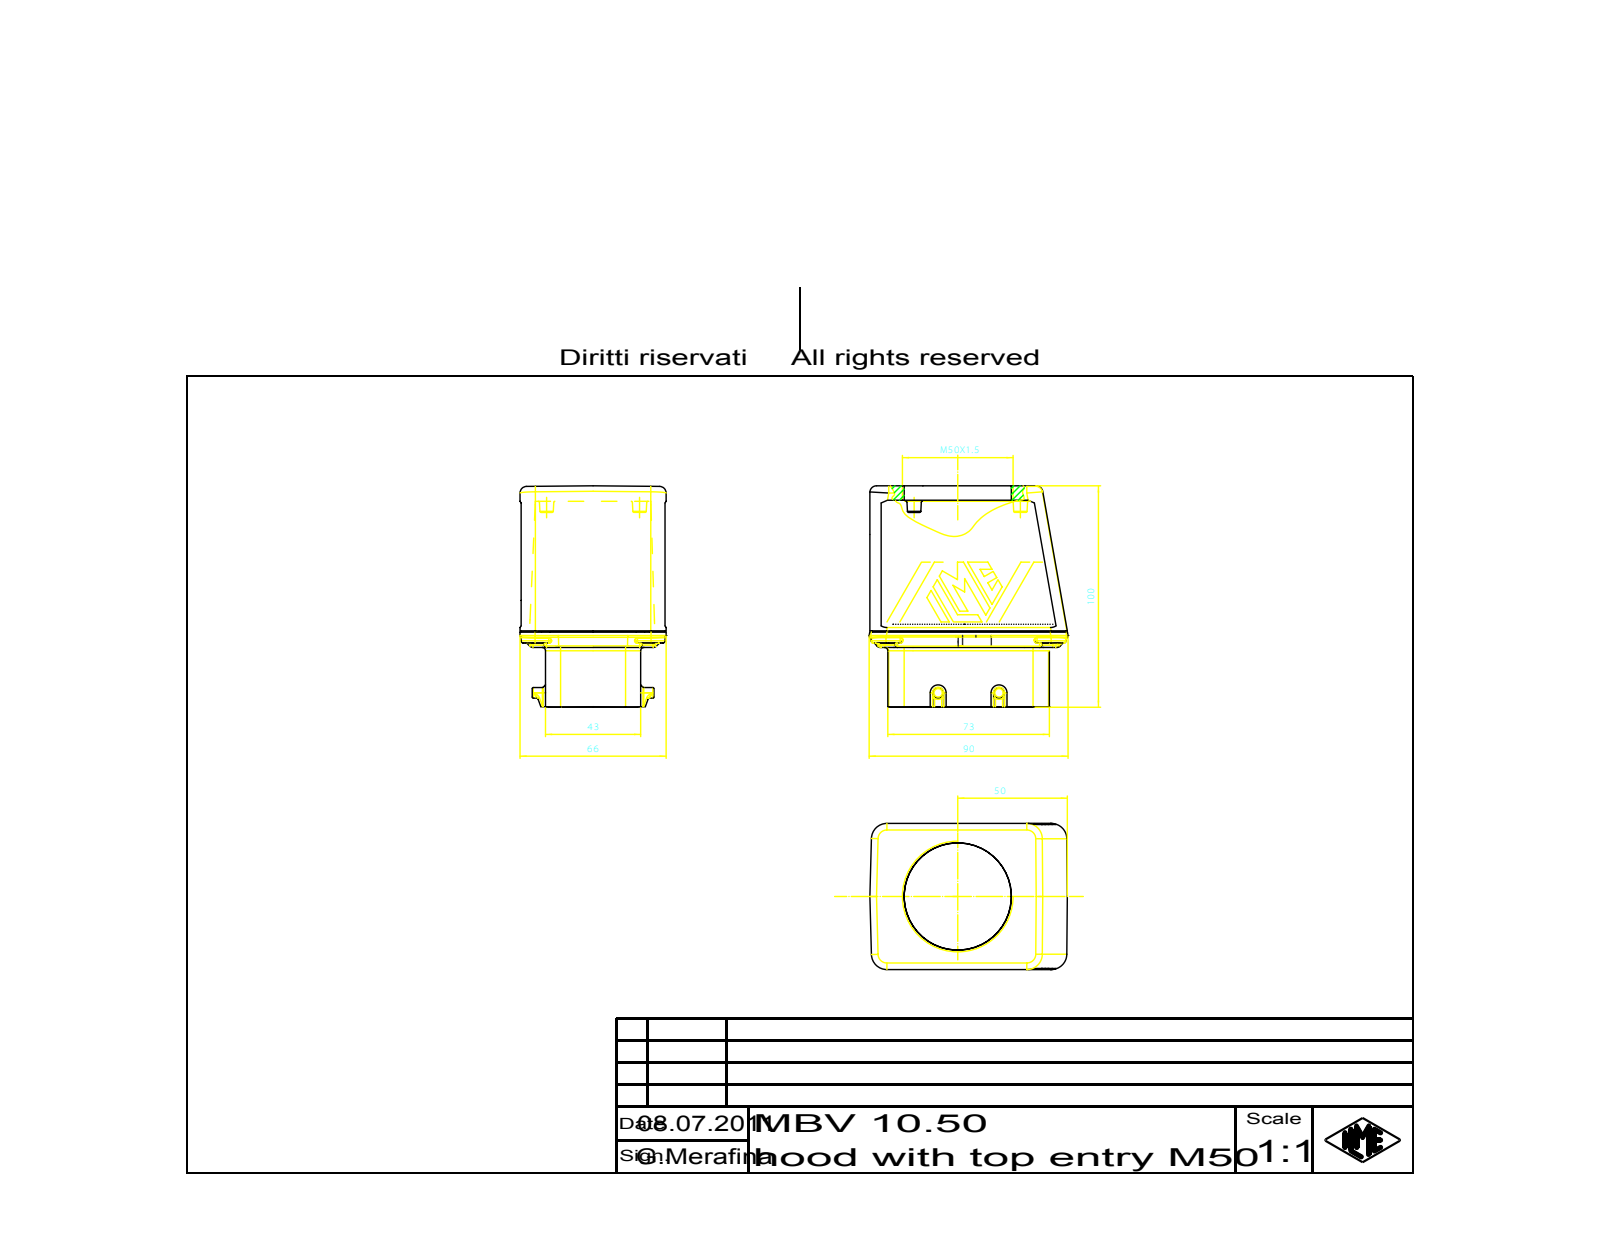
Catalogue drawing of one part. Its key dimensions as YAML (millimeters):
part_name: "53848_Body_1_Body_1.1"
step_written_by: "CoCreate Modeling 16.00A 16-Aug-2008 (C) Parametric Technology GmbH (AUTOMOTIVE_DESIGN)"
units: millimeters
bodies: {solids: 1, faces: 609, planar: 297, cylindrical: 148, other: 164}
overall_size: [99.49, 88.76, 66.01]
volume: 360273
surface_area: 47706
round_holes:
  - {diameter: 50, count: 1}
round_bosses_or_shafts:
  - {diameter: 4.8, count: 2}
partial_cylinders:
  - {radius: 1, count: 46}
  - {radius: 0.3, count: 18}
  - {radius: 7, count: 12}
  - {radius: 3, count: 10}
  - {radius: 0.5, count: 8}
  - {radius: 1.5, count: 6}
  - {radius: 4.2, count: 4}
  - {radius: 5, count: 4}
face_to_face_distances: [65.01, 72.73, 0.4, 65.41, 25, 47.73, 11, 54.01, 54, 43]
